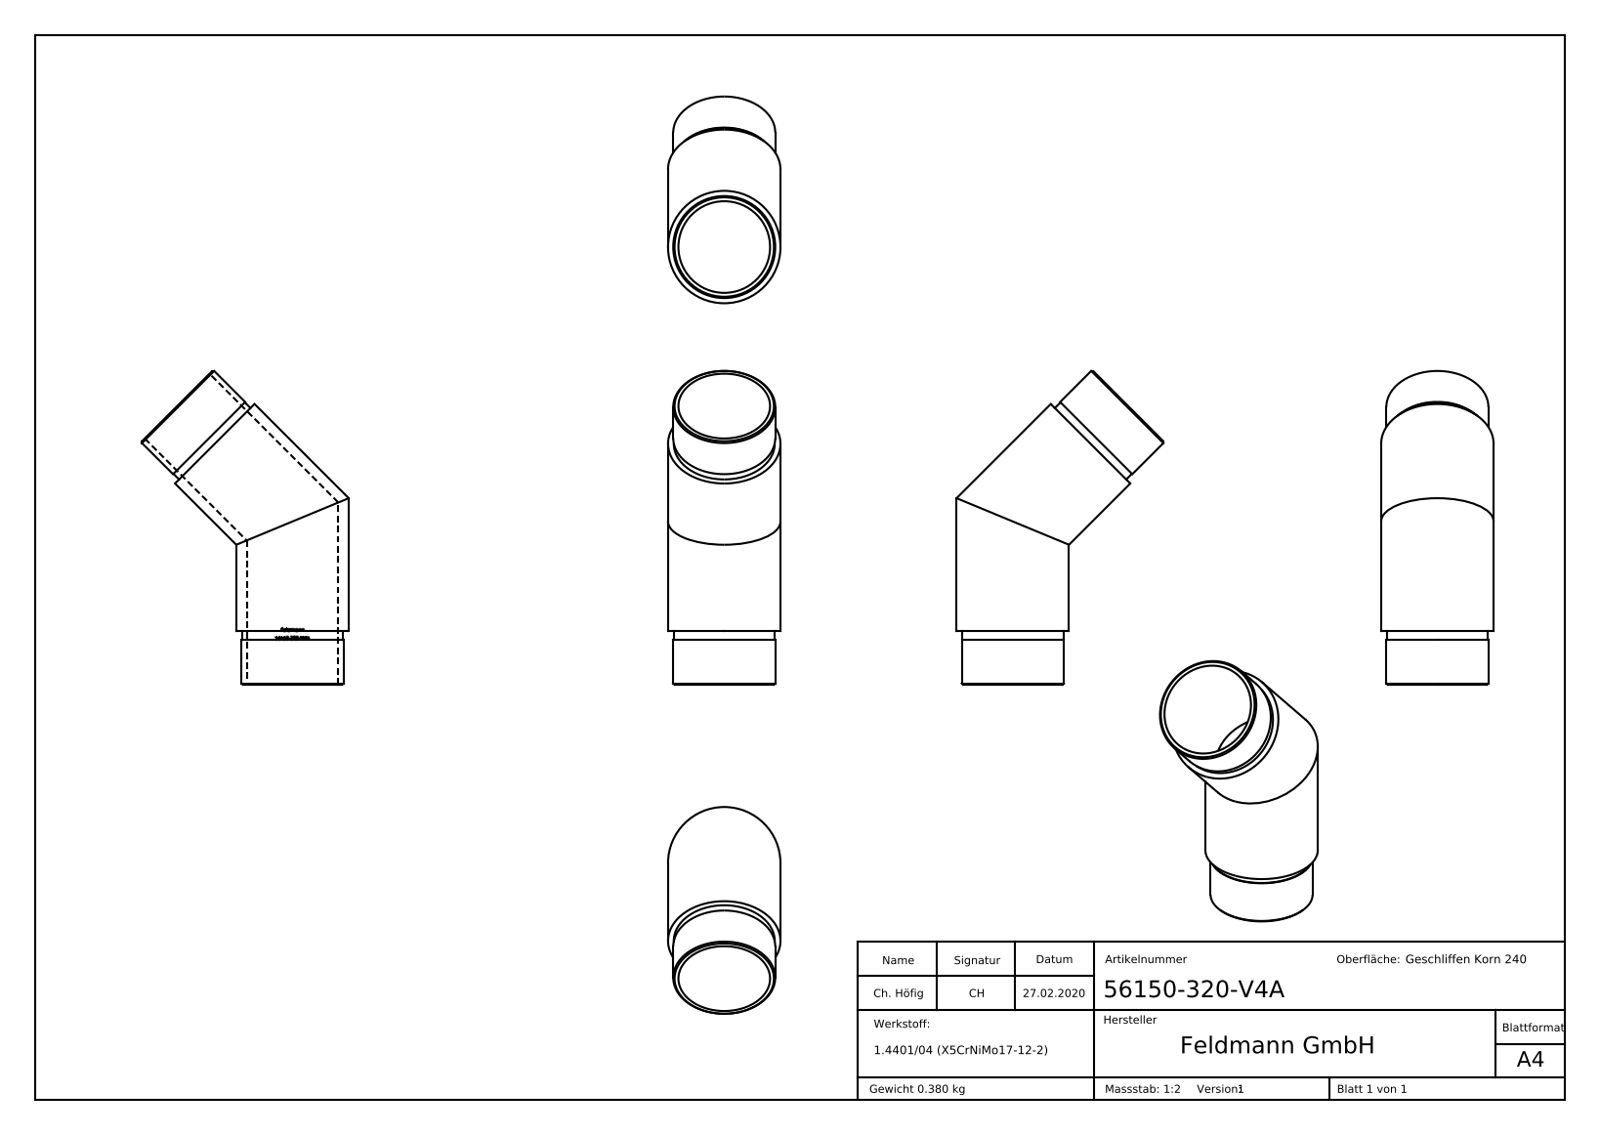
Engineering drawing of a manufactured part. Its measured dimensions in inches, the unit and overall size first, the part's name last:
Units: inches
Overall size (bounding box): 4.637 × 3.056 × 1.661
Round holes (diameter × count): ⌀1.354 ×2
Round bosses / shafts (diameter × count): ⌀1.661 ×2, ⌀1.508 ×2, ⌀1.492 ×2
Partial cylindrical surfaces — rounded edges, fillets, slot ends (radius × count): R0.681 ×1
Main face-to-face distances: 0.787, 0.669, 0.118, 0.052, 0.044, 0.161, 0.117, 0.065, 0.074, 0.132
Volume: 2.896 in³ · Surface area: 46.44 in²
Bodies: 1 solid, 279 faces (129 planar, 37 cylindrical, 113 other)
Part name (STEP PRODUCT): 56150-320-V4A
STEP written by: SolidWorks 2015 (CONFIG_CONTROL_DESIGN)
